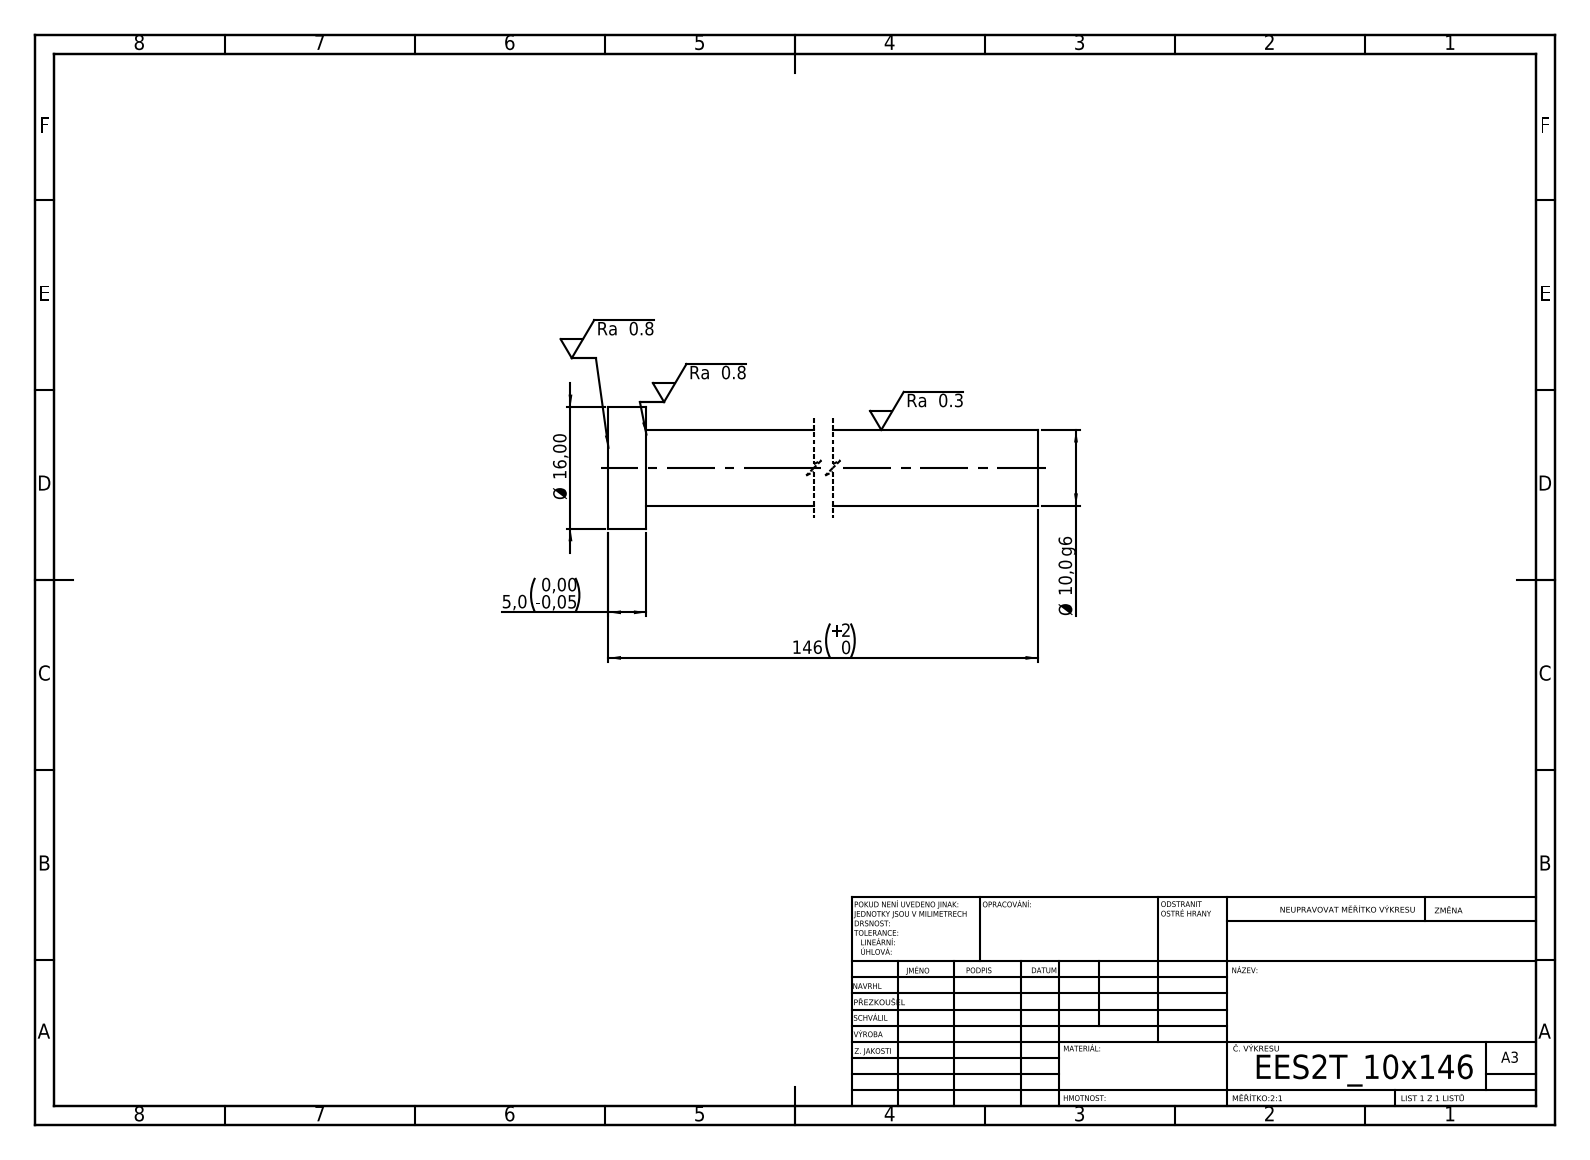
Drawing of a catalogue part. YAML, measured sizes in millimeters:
step_written_by: "SolidWorks 2019 (CONFIG_CONTROL_DESIGN)"
units: millimeters
bodies: {solids: 1, faces: 7, planar: 3, cylindrical: 4, other: 0}
overall_size: [146, 16, 16]
volume: 12079
surface_area: 5083
round_bosses_or_shafts:
  - {diameter: 16, count: 1}
  - {diameter: 10, count: 1}
face_to_face_distances: [5, 146, 141]
